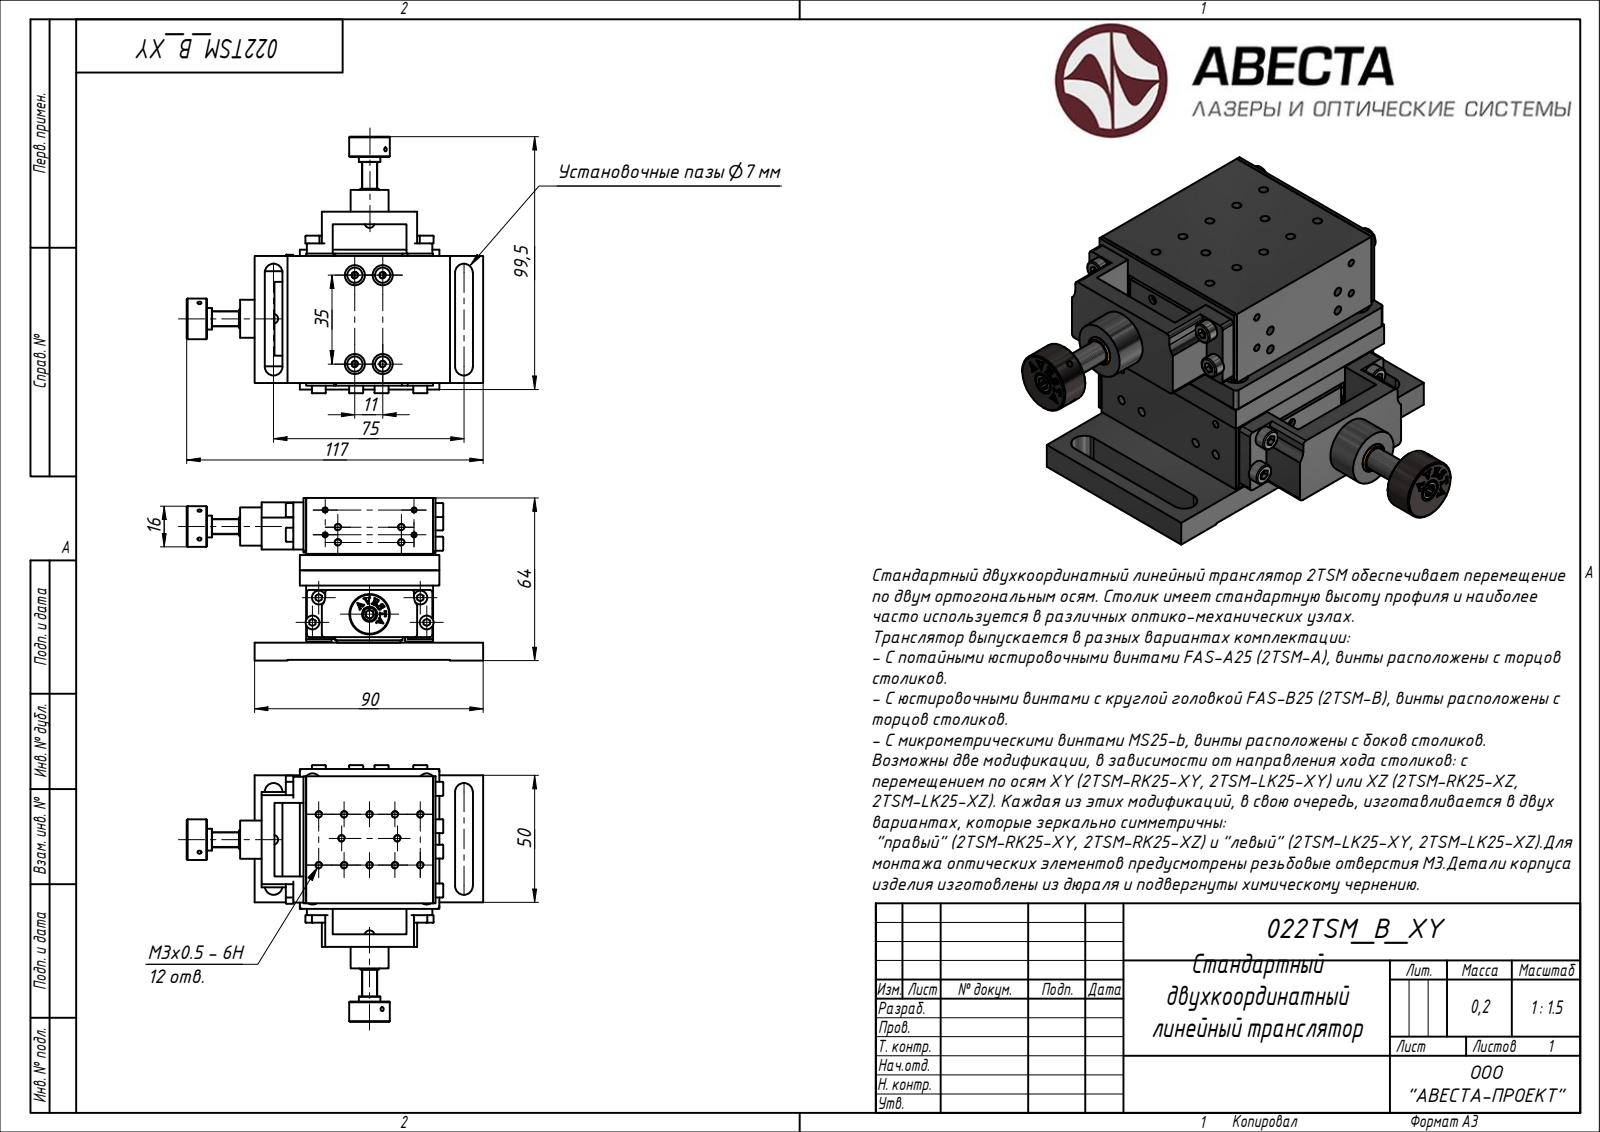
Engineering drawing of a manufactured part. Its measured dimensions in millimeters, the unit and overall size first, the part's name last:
Units: millimetres
Overall size (bounding box): 116.7 × 100 × 64
Bodies: 24 solids, 1530 faces (0 planar, 0 cylindrical, 1530 other)
STEP written by: ST-DEVELOPER v15 (AUTOMOTIVE_DESIGN)
